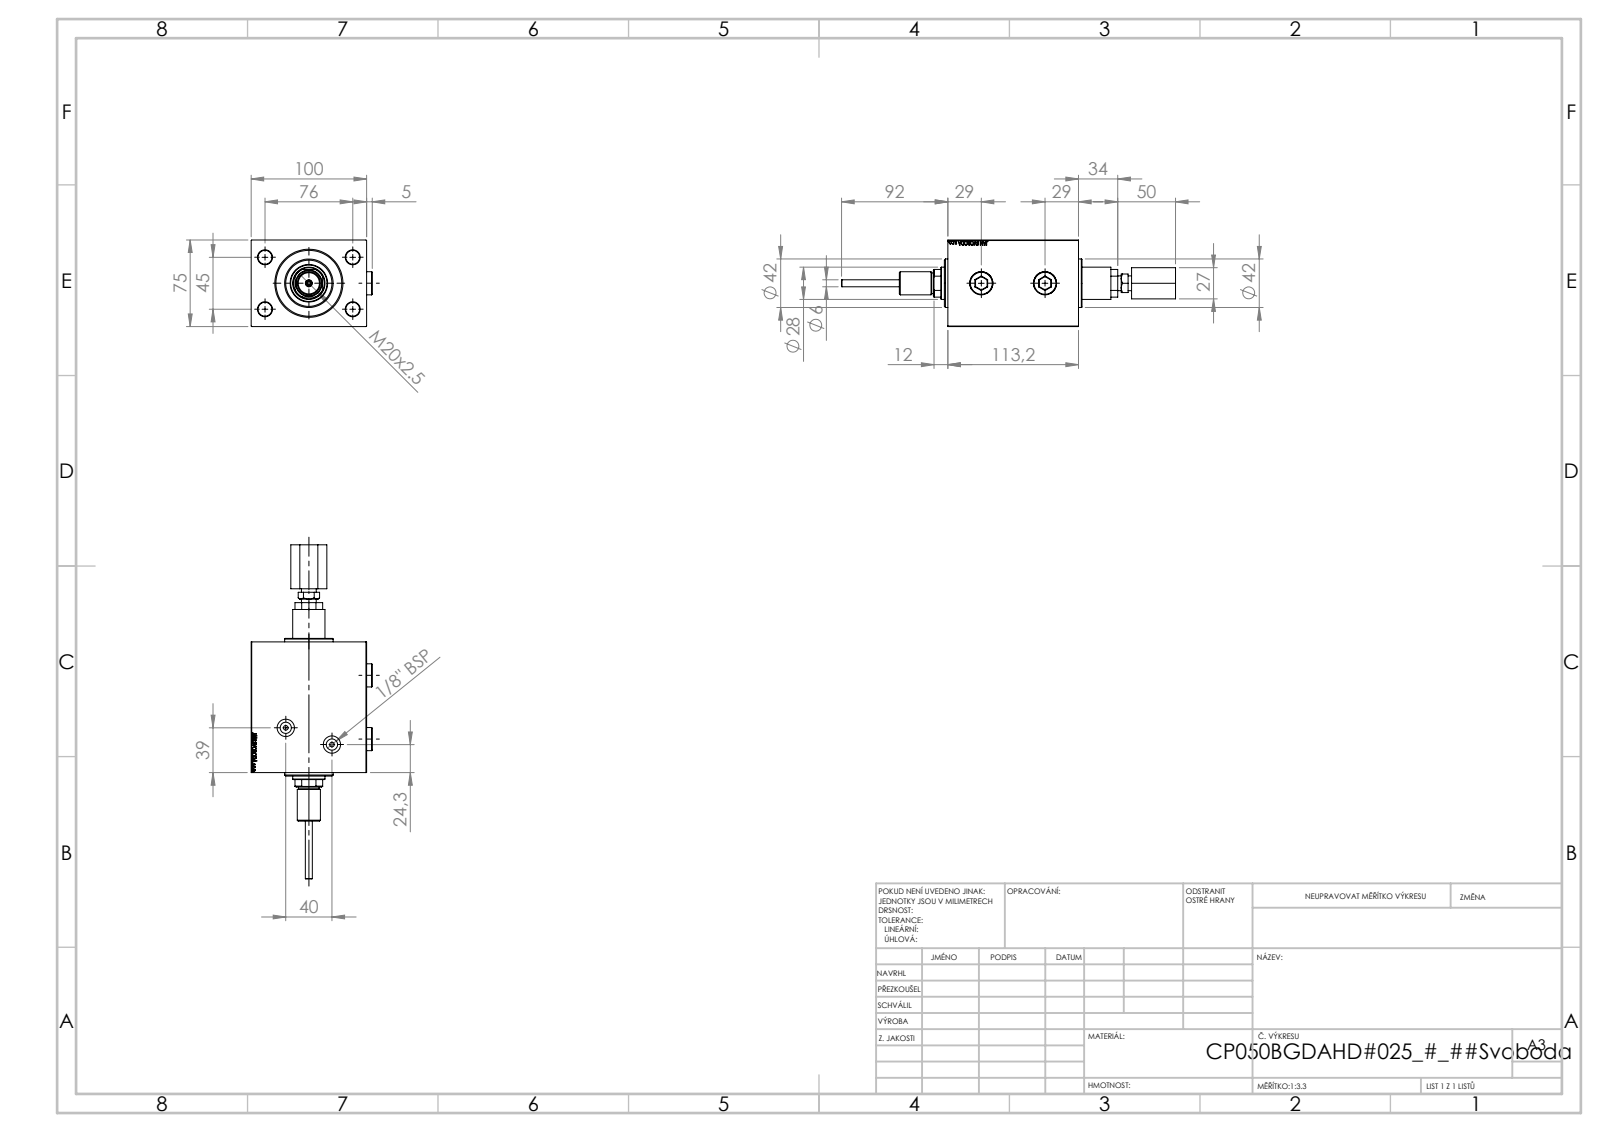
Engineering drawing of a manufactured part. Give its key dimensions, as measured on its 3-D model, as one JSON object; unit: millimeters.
{"part_name": "V450DCP_B_RodCooling_ACCESSORIES; V450DCP_VC_B; V450DCP_B_VCP; V450DCP_B_Body (+2 more)", "step_written_by": "SolidWorks 2019 (CONFIG_CONTROL_DESIGN)", "units": "millimeters", "bodies": {"solids": 7, "faces": 1040, "planar": 472, "cylindrical": 114, "other": 454}, "overall_size": [289.2, 104.9, 75], "volume_mm3": 847920, "surface_area_mm2": 135990, "round_holes": [[12, 4], [5, 3], [13.16, 3], [20, 3], [4, 2], [9.73, 2], [15, 2], [3, 1], [6, 1], [18.5, 1], [28, 1], [31.5, 1]], "round_bosses_or_shafts": [[42, 1], [20, 1], [18, 1], [12.78, 1]], "partial_cylinders_radius": [[13.5, 1]], "face_to_face_distances": [75, 100, 113.2, 14, 99.2, 13, 43, 1, 27, 112.2], "hole_center_spacings": [44.16, 45, 76, 88.32, 11, 42.55, 55.2, 66.2]}
